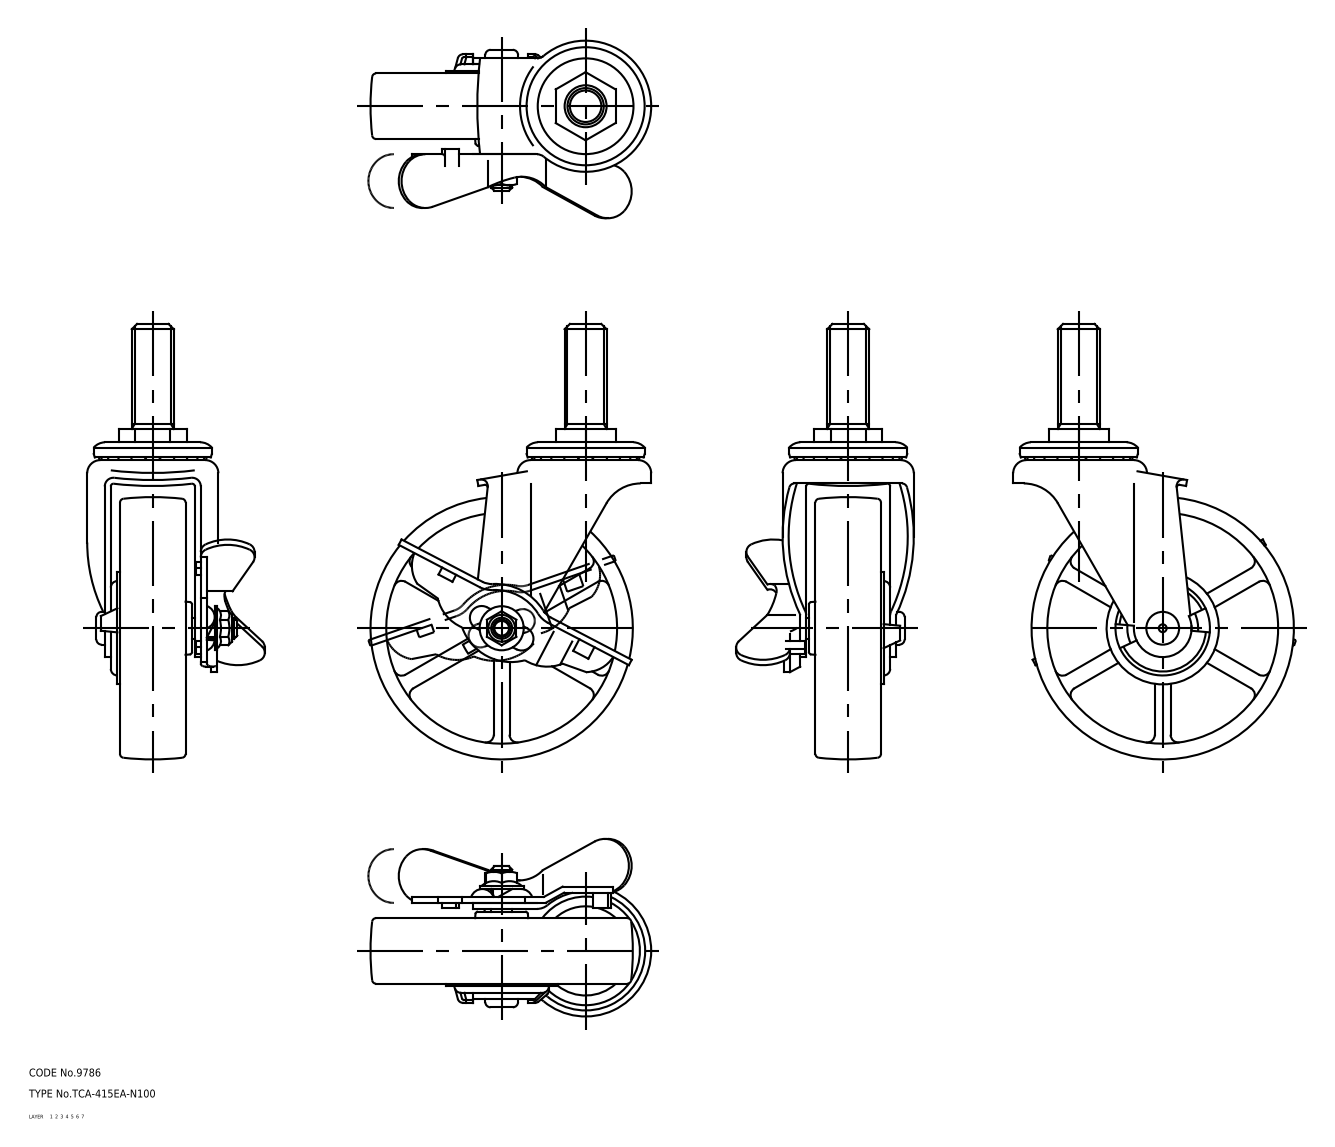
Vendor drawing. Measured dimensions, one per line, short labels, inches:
name: wheel; mounting plate; main shaft; lever (+2 more)
written by: CADfix (AUTOMOTIVE_DESIGN)
unit: in
bodies: 6 solids, 643 faces (0 planar, 0 cylindrical, 643 other)
size: 6.535 × 4.213 × 2.665
volume: 11.94 in³; area: 101.6 in²
